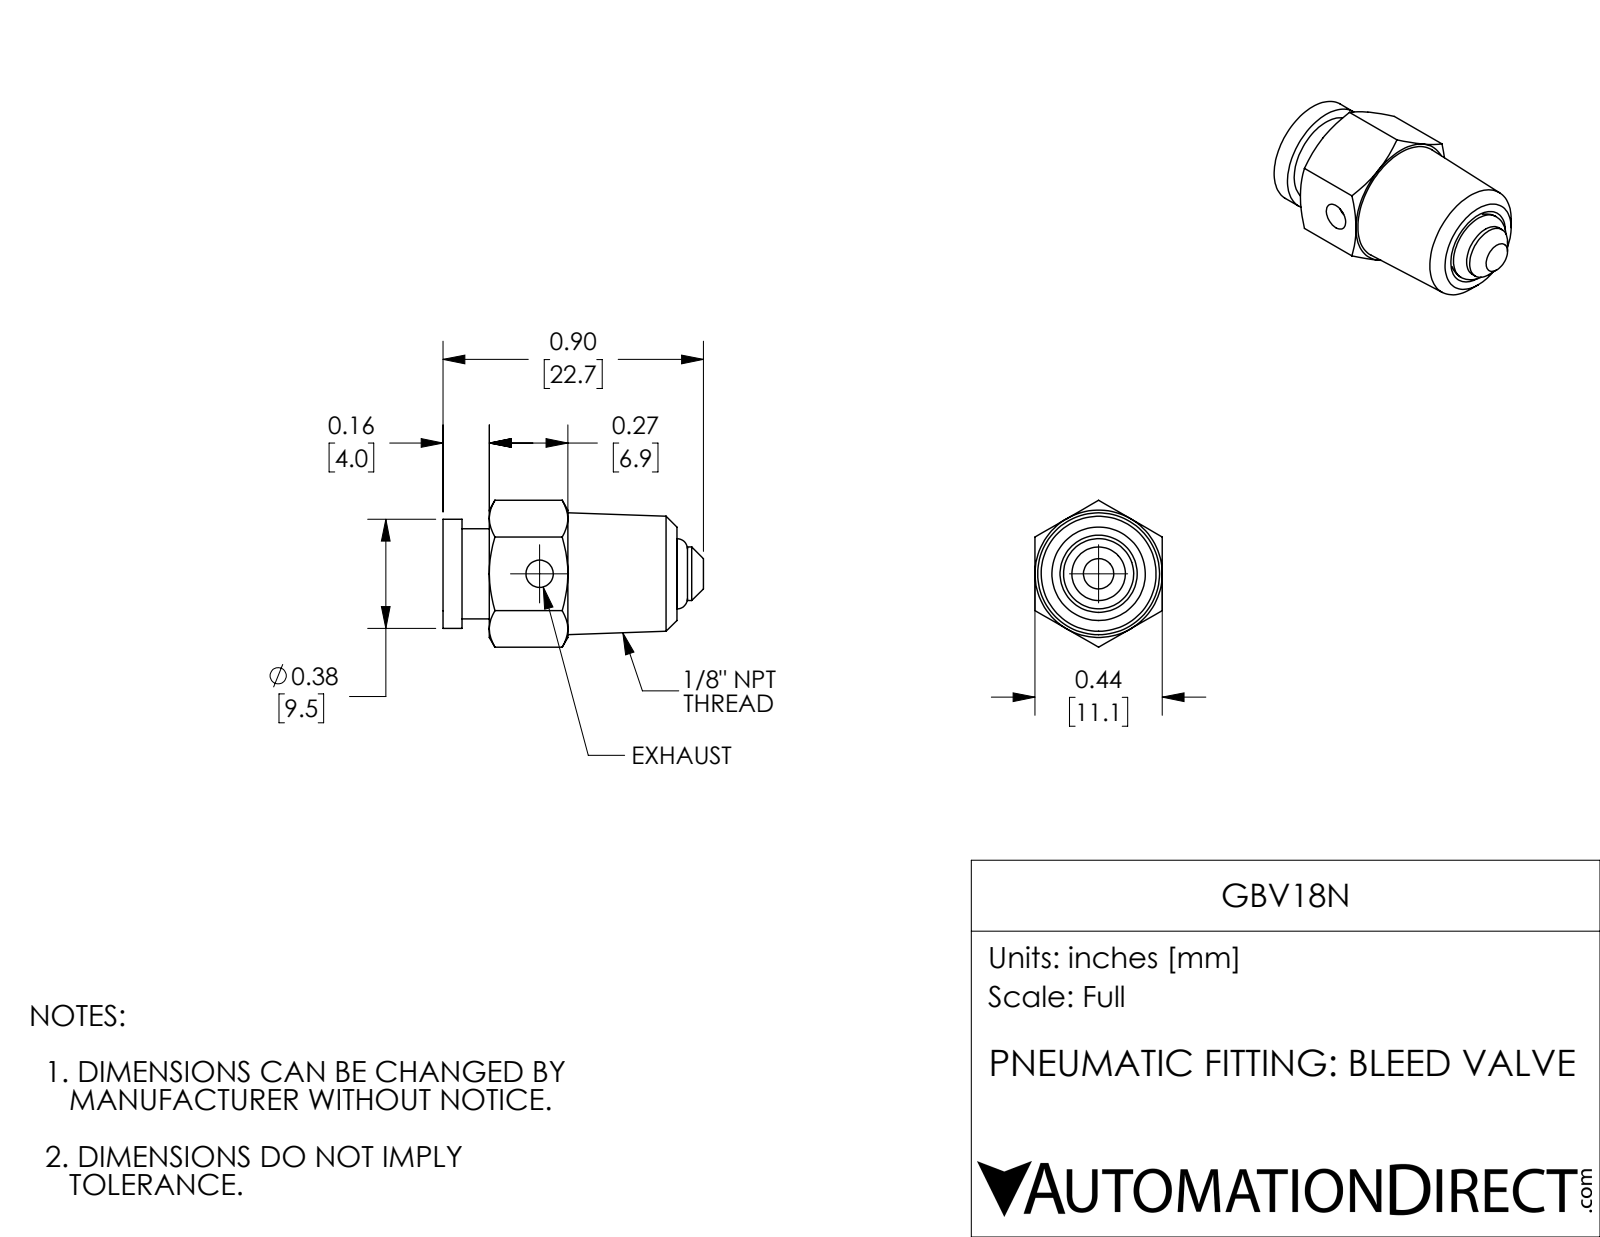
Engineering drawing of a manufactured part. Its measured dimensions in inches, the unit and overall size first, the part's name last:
Units: inches
Overall size (bounding box): 0.895 × 0.505 × 0.438
Round holes (diameter × count): ⌀0.094 ×1, ⌀0.316 ×1
Round bosses / shafts (diameter × count): ⌀0.375 ×1, ⌀0.31 ×1, ⌀0.184 ×1
Main face-to-face distances: 0.438, 0.379, 0.185, 0.194, 0.159, 0.026, 0.22, 0.065, 0.094, 0.12
Volume: 0.092 in³ · Surface area: 1.996 in²
Bodies: 4 solids, 52 faces (16 planar, 10 cylindrical, 26 other)
Part name (STEP PRODUCT): GBV18N
STEP written by: SolidWorks 2018 (AUTOMOTIVE_DESIGN)
